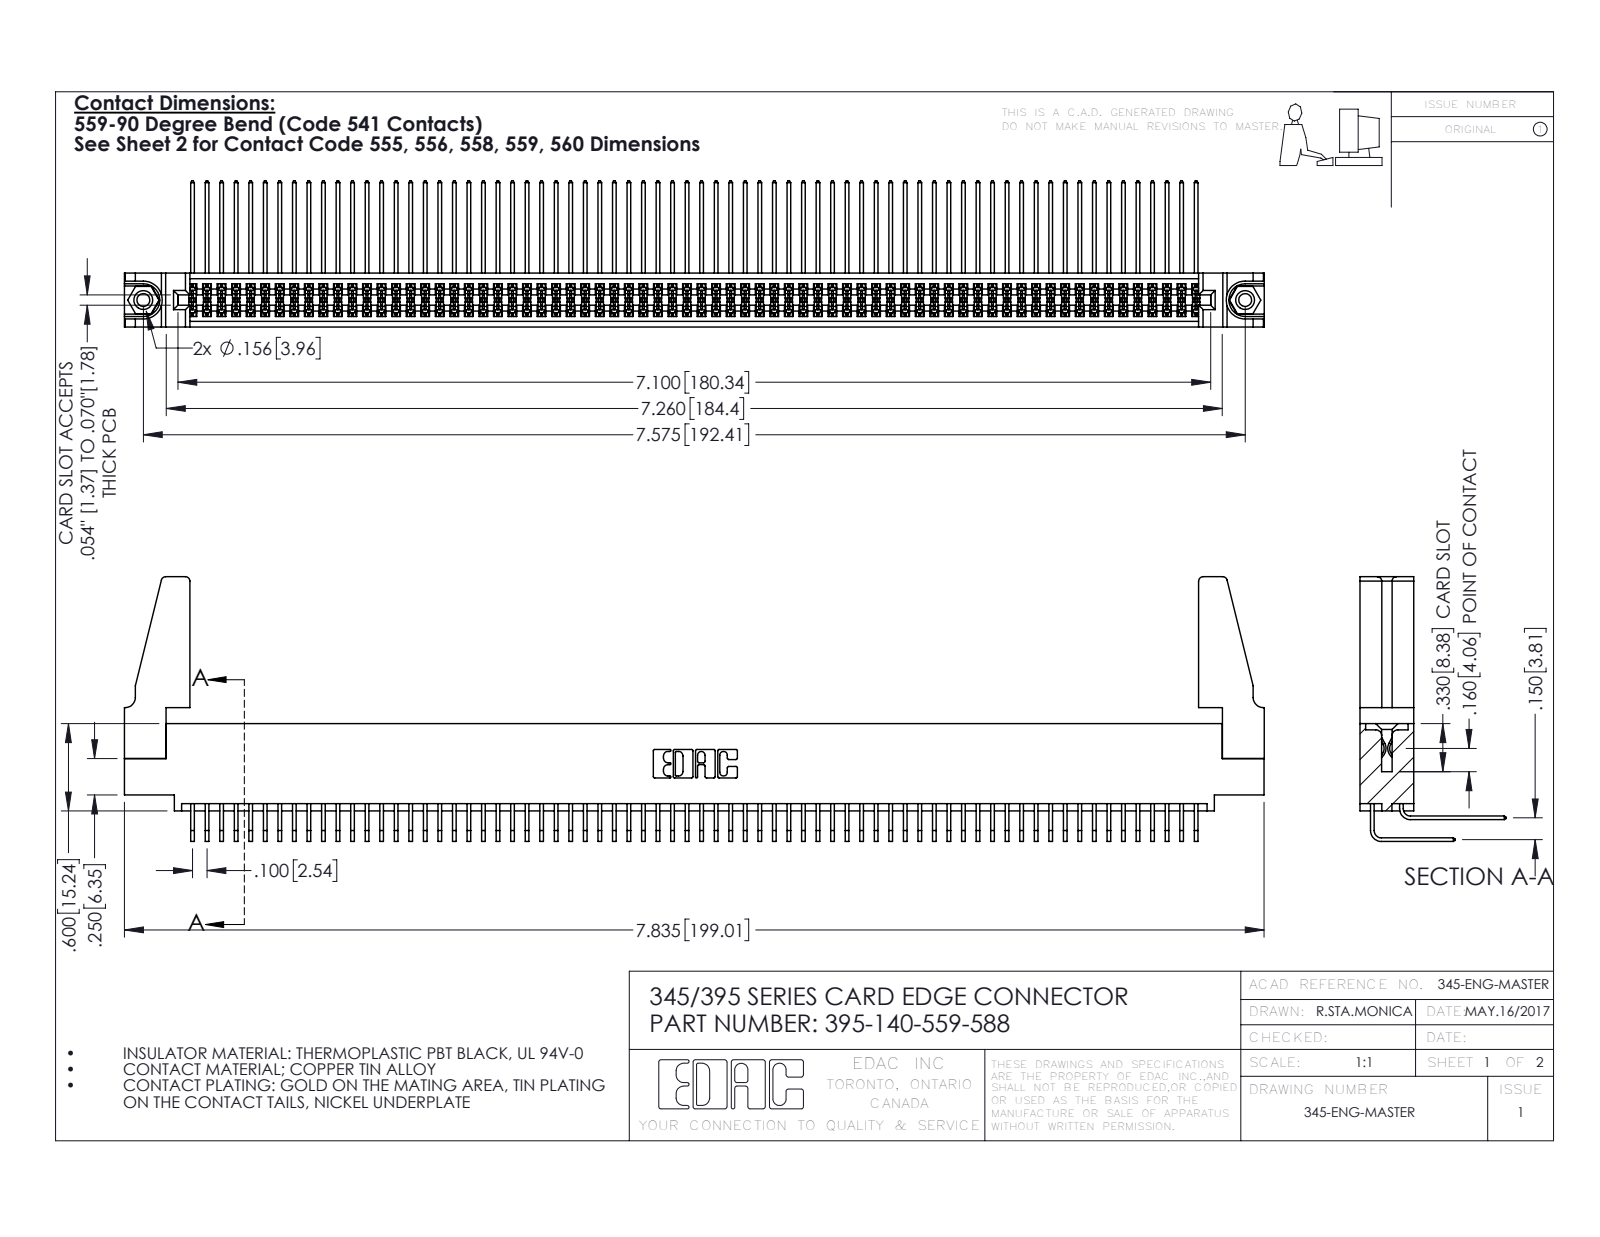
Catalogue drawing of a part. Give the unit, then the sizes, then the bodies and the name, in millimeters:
Units: millimetres
Overall size (bounding box): 199 × 46.2 × 25.5
Round holes (diameter × count): ⌀2.3 ×2, ⌀3.2 ×2, ⌀4 ×2, ⌀1.6 ×1
Round bosses / shafts (diameter × count): ⌀3.9 ×2
Partial cylindrical surfaces — rounded edges, fillets, slot ends (radius × count): R0.2 ×279, R0.3 ×22, R0.8 ×8, R0.2 ×6, R0.8 ×6, R0.7 ×3, R0.4 ×2, R0.5 ×2
Main face-to-face distances: 1.8, 7.6, 9.4, 5.1, 2.5, 6.9, 0.6, 5.7, 4.4, 3.8
Hole centre spacings: 6.9, 186.4, 192.4
Volume: 23 580 mm³ · Surface area: 37 610 mm²
Bodies: 145 solids, 7534 faces (5056 planar, 2462 cylindrical, 16 other)
Part name (STEP PRODUCT): 345-292-001_558 559 Tail - 1; 395-140-559-588; 345 Part_0.110 Offset - 0.156 Dia-TH; 345-220-078_345-220-088 (+2 more)
STEP written by: SolidWorks 2016 (CONFIG_CONTROL_DESIGN)
